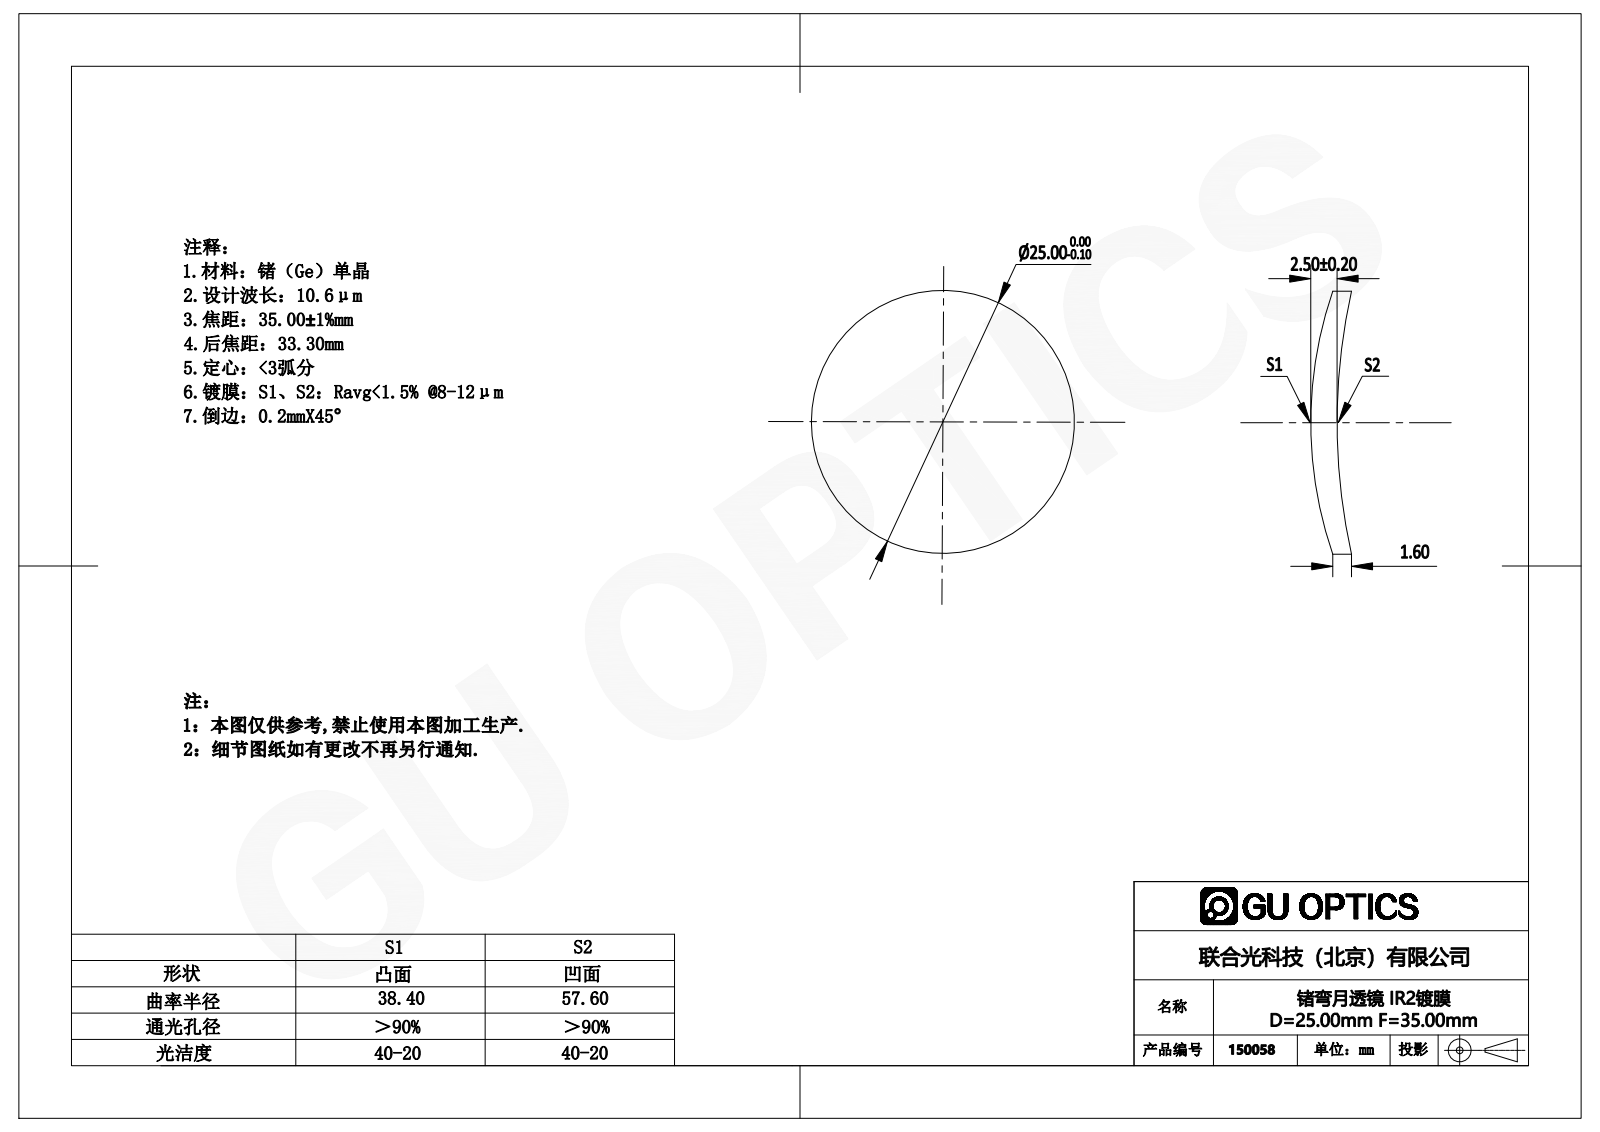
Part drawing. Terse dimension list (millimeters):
name: 150052
written by: SolidWorks 2016 (AUTOMOTIVE_DESIGN)
unit: mm
bodies: 1 solid, 6 faces (0 planar, 2 cylindrical, 4 other)
size: 25 × 25 × 3.87
volume: 1 054 mm³; area: 1 141 mm²
bosses: 1× ⌀25
